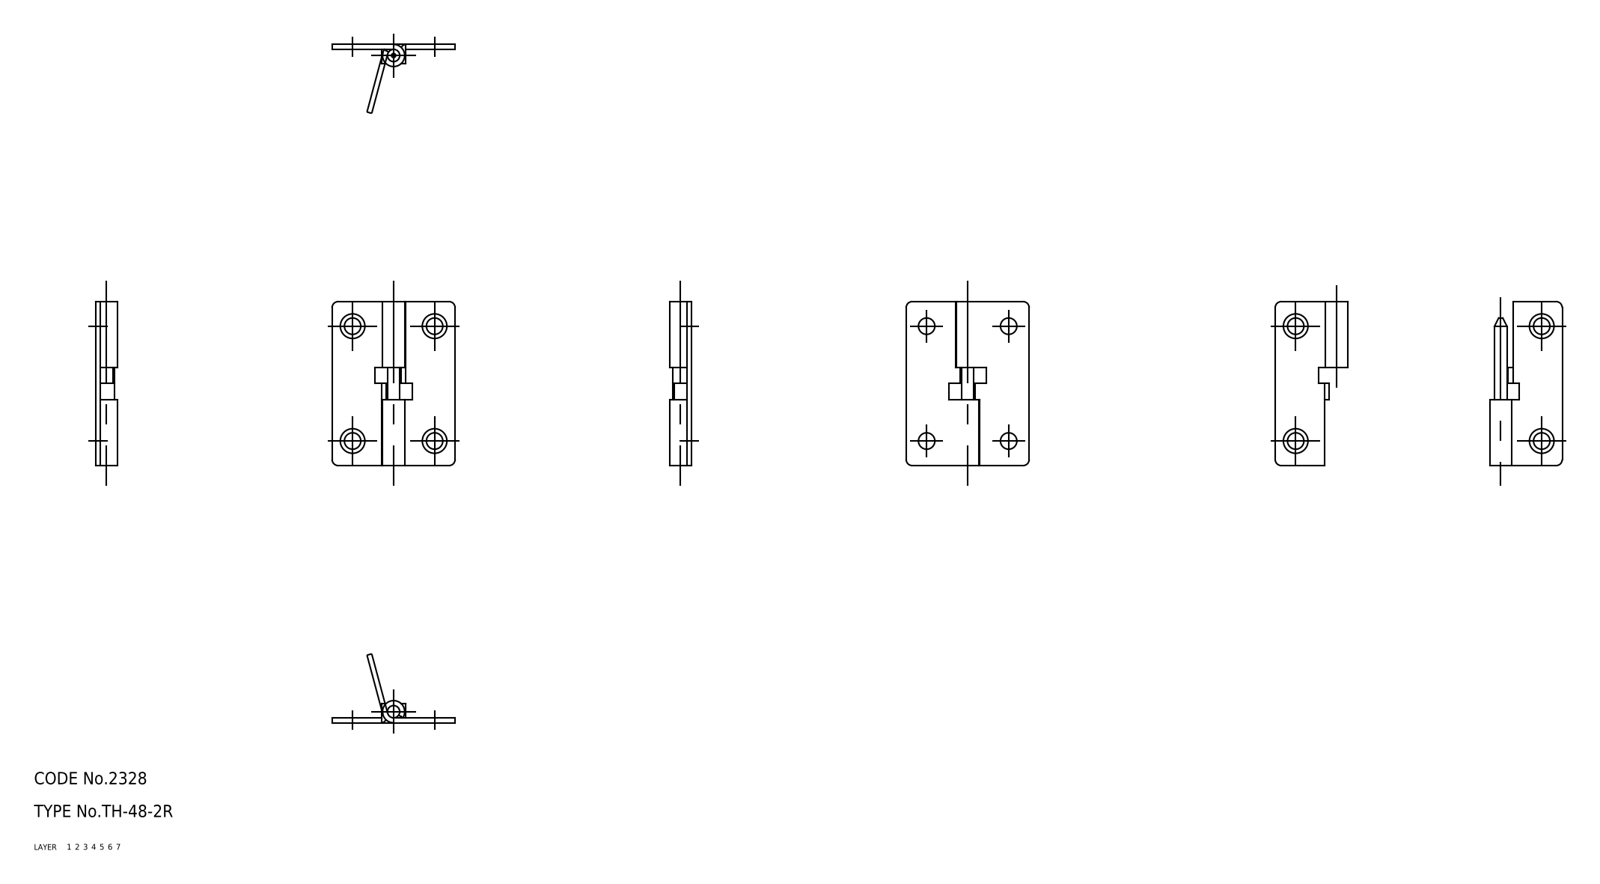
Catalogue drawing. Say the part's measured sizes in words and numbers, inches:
The part is named "shaft; hinge piece_B; hinge piece_A; TH_48_2R_10257_36". Its 3-D file was written by "CADfix (AUTOMOTIVE_DESIGN)". It is 3 solids with 60 faces: 0 planar, 0 cylindrical and 60 other. Overall it measures 1.575 by 1.181 by 0.213 inches. Its volume is 0.114 cubic inches and its surface area 5.399 square inches.
